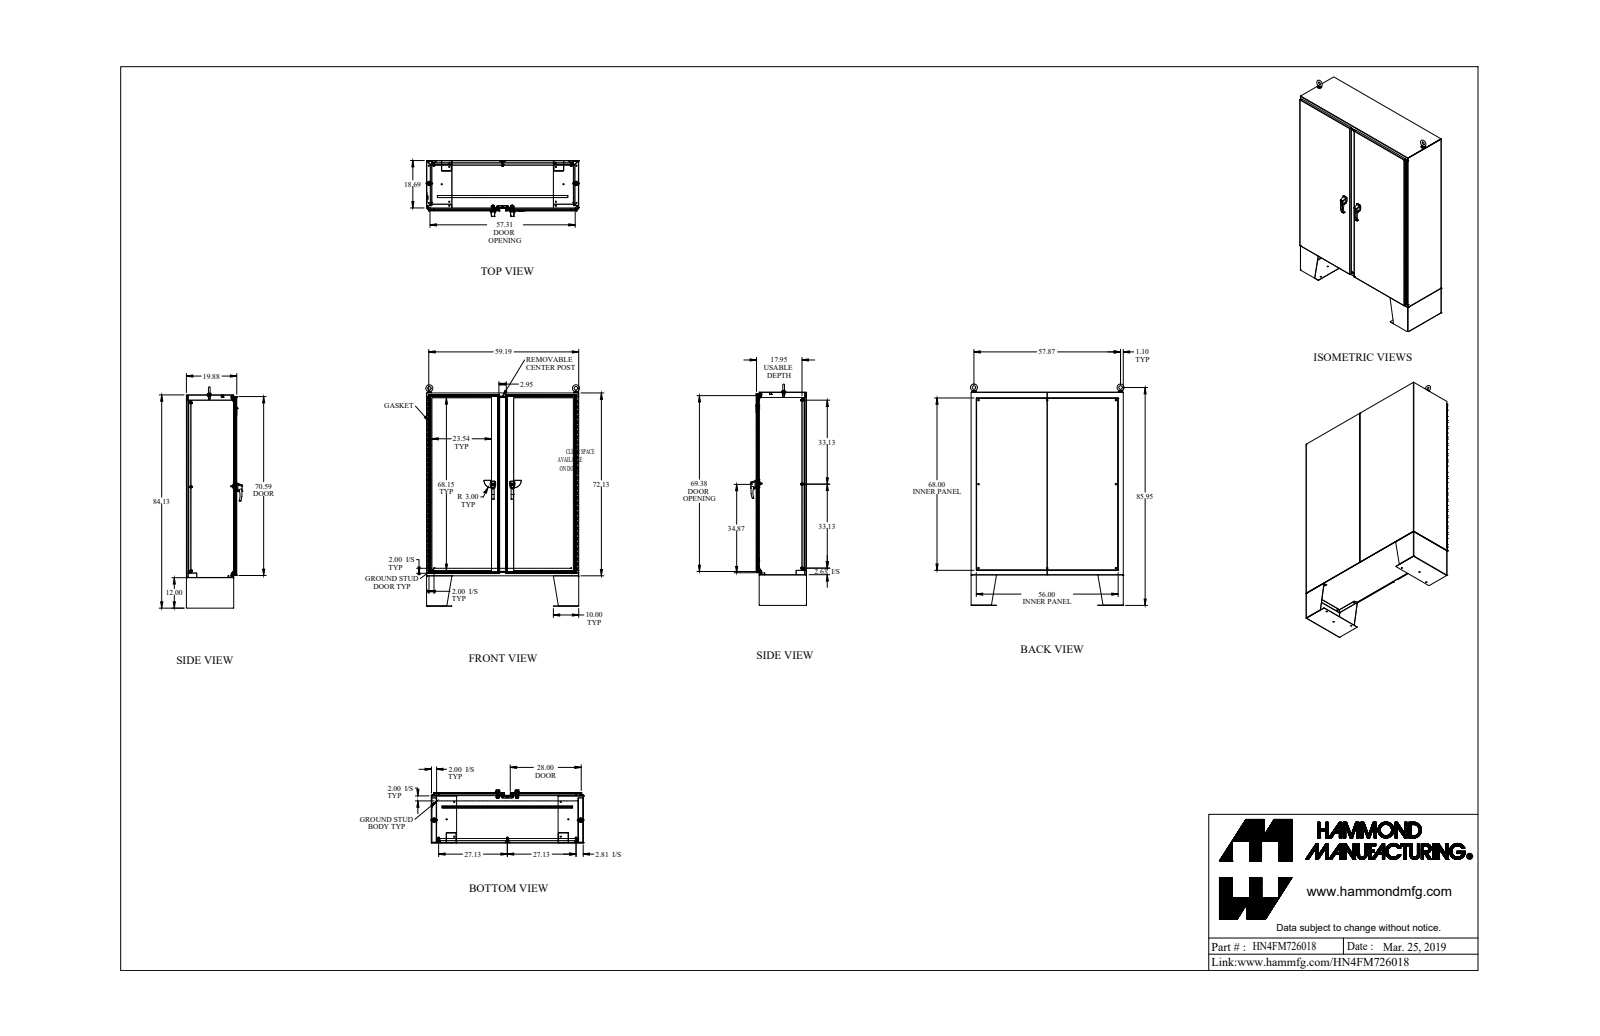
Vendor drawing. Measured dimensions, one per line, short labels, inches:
name: HN4FM726018
written by: SolidWorks 2018 (AUTOMOTIVE_DESIGN)
unit: in
bodies: 131 solids, 4006 faces (1830 planar, 1803 cylindrical, 373 other)
size: 87.315 × 60.607 × 21.99
volume: 2 238 in³; area: 44 911 in²
holes: 24× ⌀0.304, 14× ⌀0.437, 8× ⌀0.307, 8× ⌀0.35, 8× ⌀0.563, 6× ⌀0.25, 6× ⌀0.445, 4× ⌀0.281, 4× ⌀0.313, 4× ⌀0.39, 3× ⌀0.201, 3× ⌀0.313
bosses: 10× ⌀1, 8× ⌀0.65, 8× ⌀0.375, 8× ⌀0.33, 8× ⌀0.281, 4× ⌀0.75, 4× ⌀0.625, 4× ⌀0.44
rounds: 33× R0.5, 32× R0.018, 32× R0.125, 29× R0.048, 29× R0.143, 28× R0.06, 12× R0.03, 12× R0.09
face distances: 0.095, 19.78, 19.685, 0.125, 17.998, 19.875, 1.782, 1.687, 18.093, 1.657
hole spacings: 6, 12, 18, 24, 30, 36, 42, 1.61
